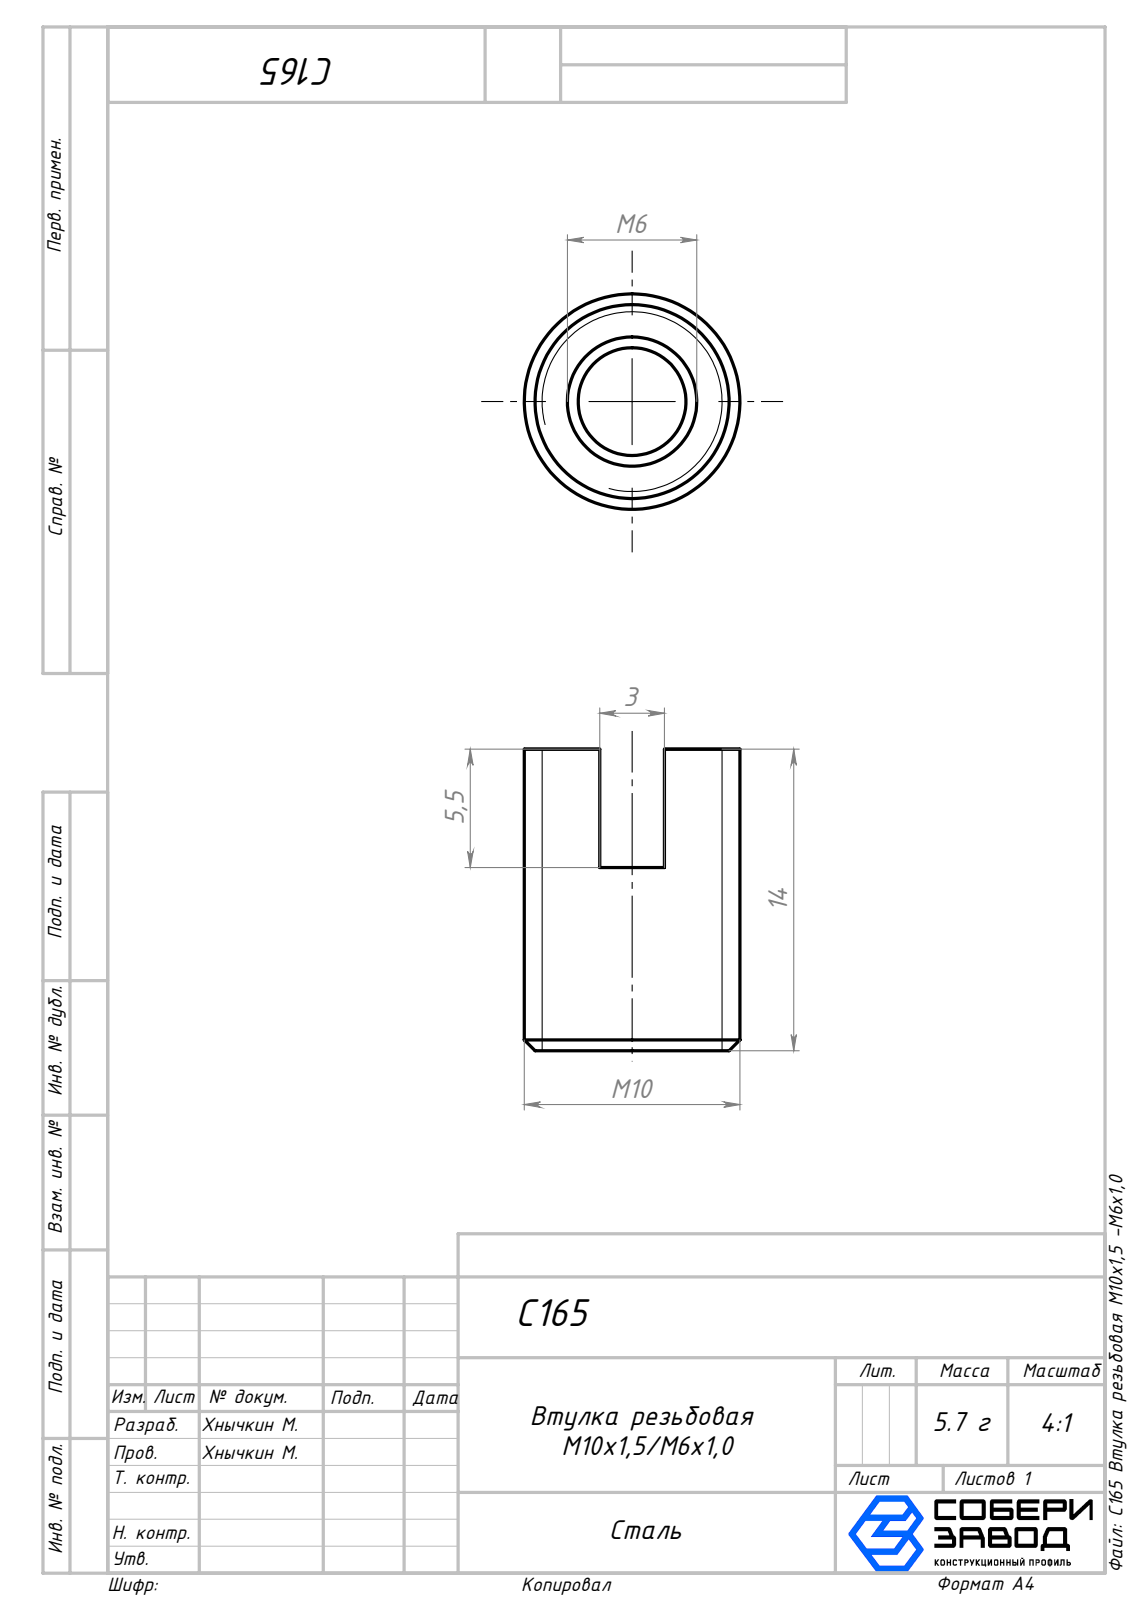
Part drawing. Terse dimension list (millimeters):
name: C165 Втулка резьбовая М10х1,5 -М6х1,0
written by: SolidWorks 2026 (AUTOMOTIVE_DESIGN)
unit: mm
bodies: 1 solid, 19 faces (9 planar, 4 cylindrical, 6 other)
size: 14 × 10 × 10
volume: 732 mm³; area: 753 mm²
holes: 1× ⌀5
bosses: 1× ⌀10
face distances: 14, 3, 8.5, 5.5
